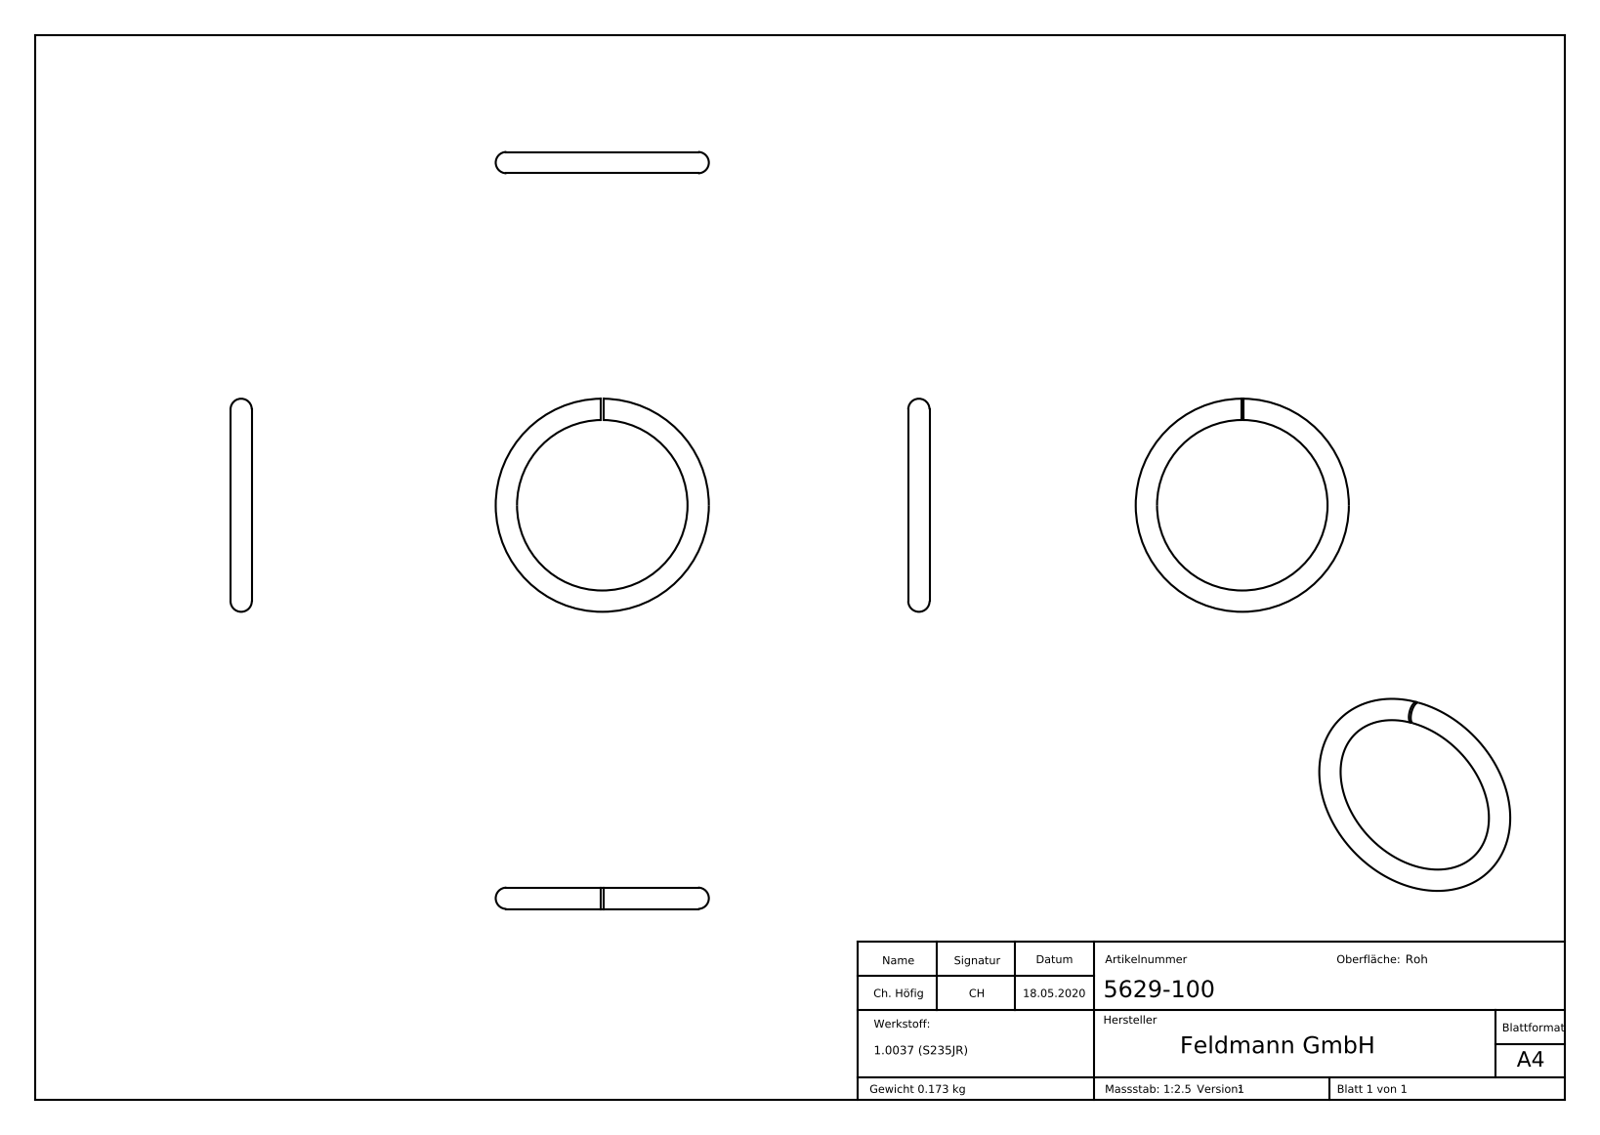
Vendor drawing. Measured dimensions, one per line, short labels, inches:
name: 5629-100
written by: SolidWorks 2015 (CONFIG_CONTROL_DESIGN)
unit: in
bodies: 1 solid, 206 faces (107 planar, 0 cylindrical, 99 other)
size: 3.937 × 3.937 × 0.394
volume: 1.35 in³; area: 14 in²
face distances: 0.039, 0.059, 0.02, 0.07, 0.083, 0.033, 0.039, 0.109, 0.096, 0.026
